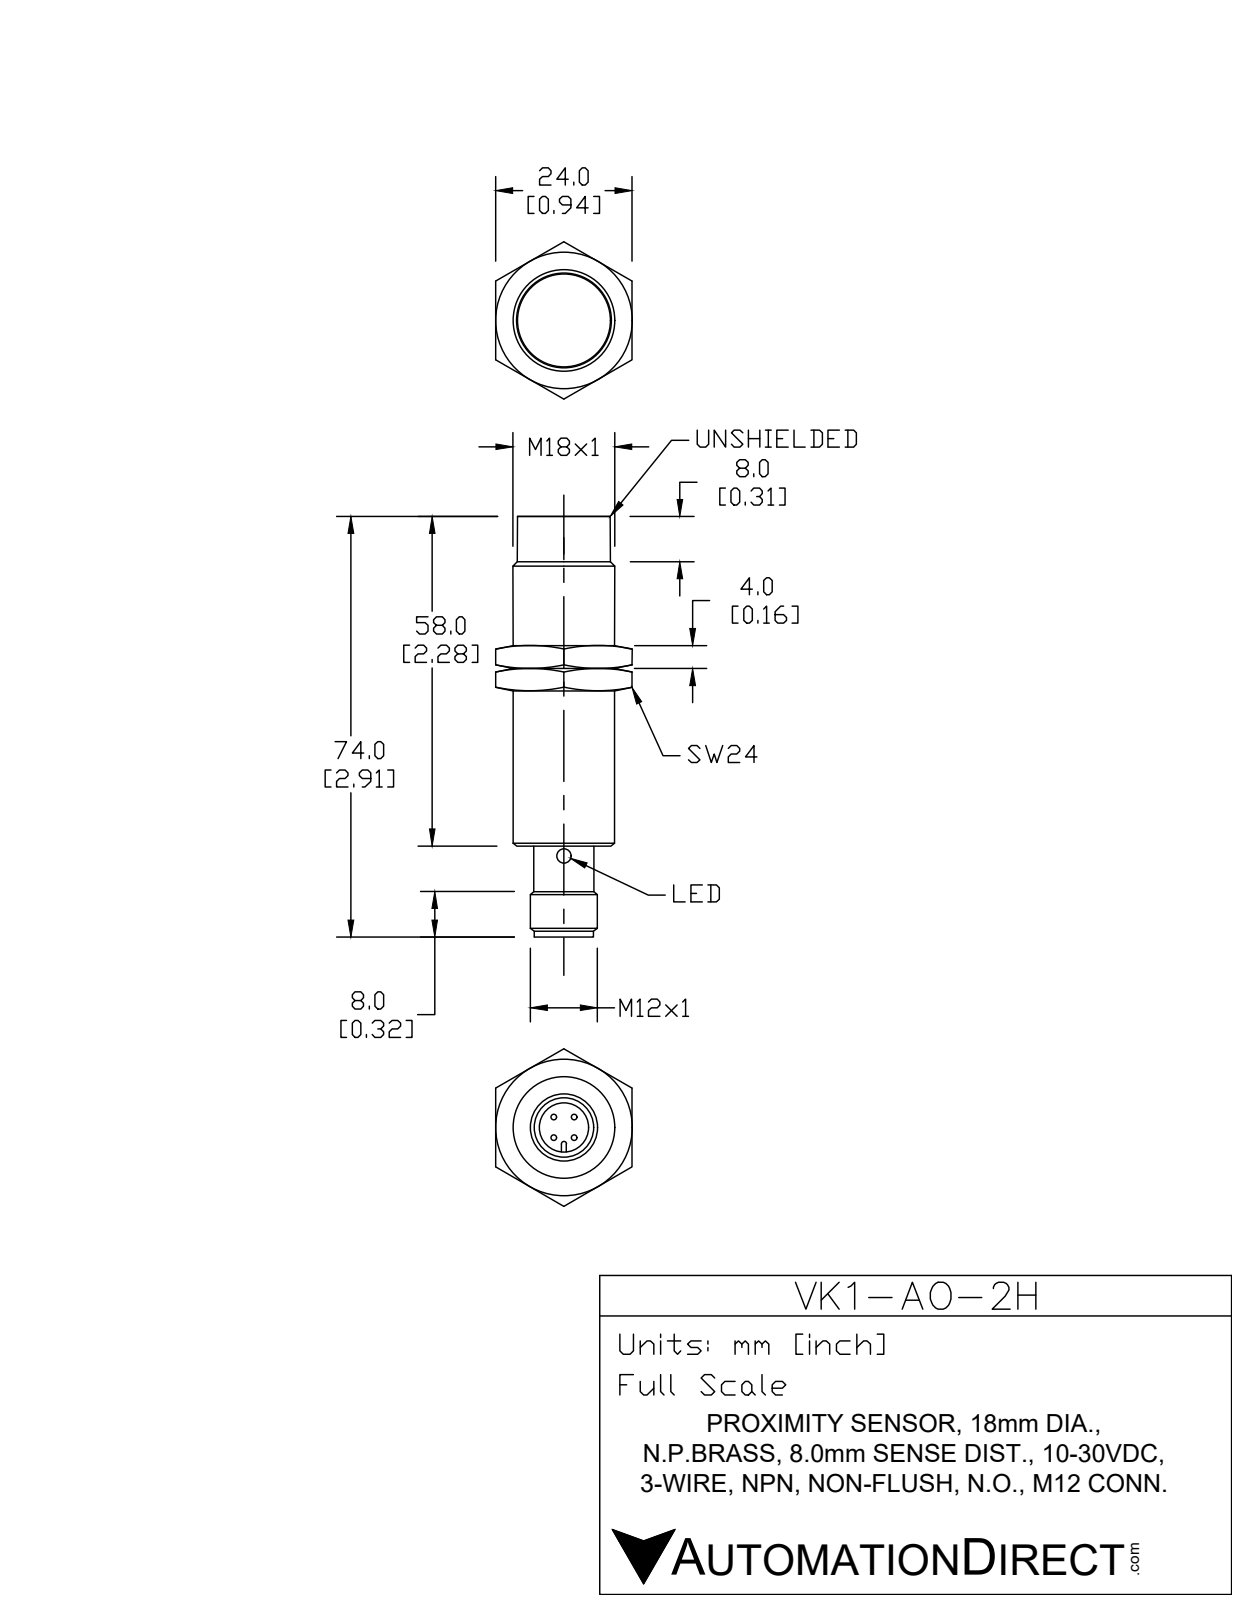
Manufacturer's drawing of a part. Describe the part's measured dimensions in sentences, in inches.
The part is named "VK1-A0-2H". Its 3-D file was written by "SolidWorks 2017 (AUTOMOTIVE_DESIGN)". It is 4 solids with 120 faces: 24 planar, 64 cylindrical and 32 other. Overall it measures 2.906 by 0.709 by 0.709 inches. Its volume is 0.93 cubic inches and its surface area 9.66 square inches. Round holes: 4 of diameter 0.098, 1 of diameter 0.331. Round bosses or shafts: 4 of diameter 0.039, 1 of diameter 0.709, 1 of diameter 0.646, 1 of diameter 0.626, 1 of diameter 0.472, 1 of diameter 0.413, 1 of diameter 0.386, 1 of diameter 0.382. Partial cylindrical surfaces (rounded edges, fillets, slot ends): 4 of radius 0.051, 1 of radius 0.02, 1 of radius 0.024, 1 of radius 0.051, 1 of radius 0.134. The main face-to-face distances are 1.949, 0.315, 2.264, 0.02, 2.283, 1.969, 2.461, 2.146, 0.197, 0.177.
